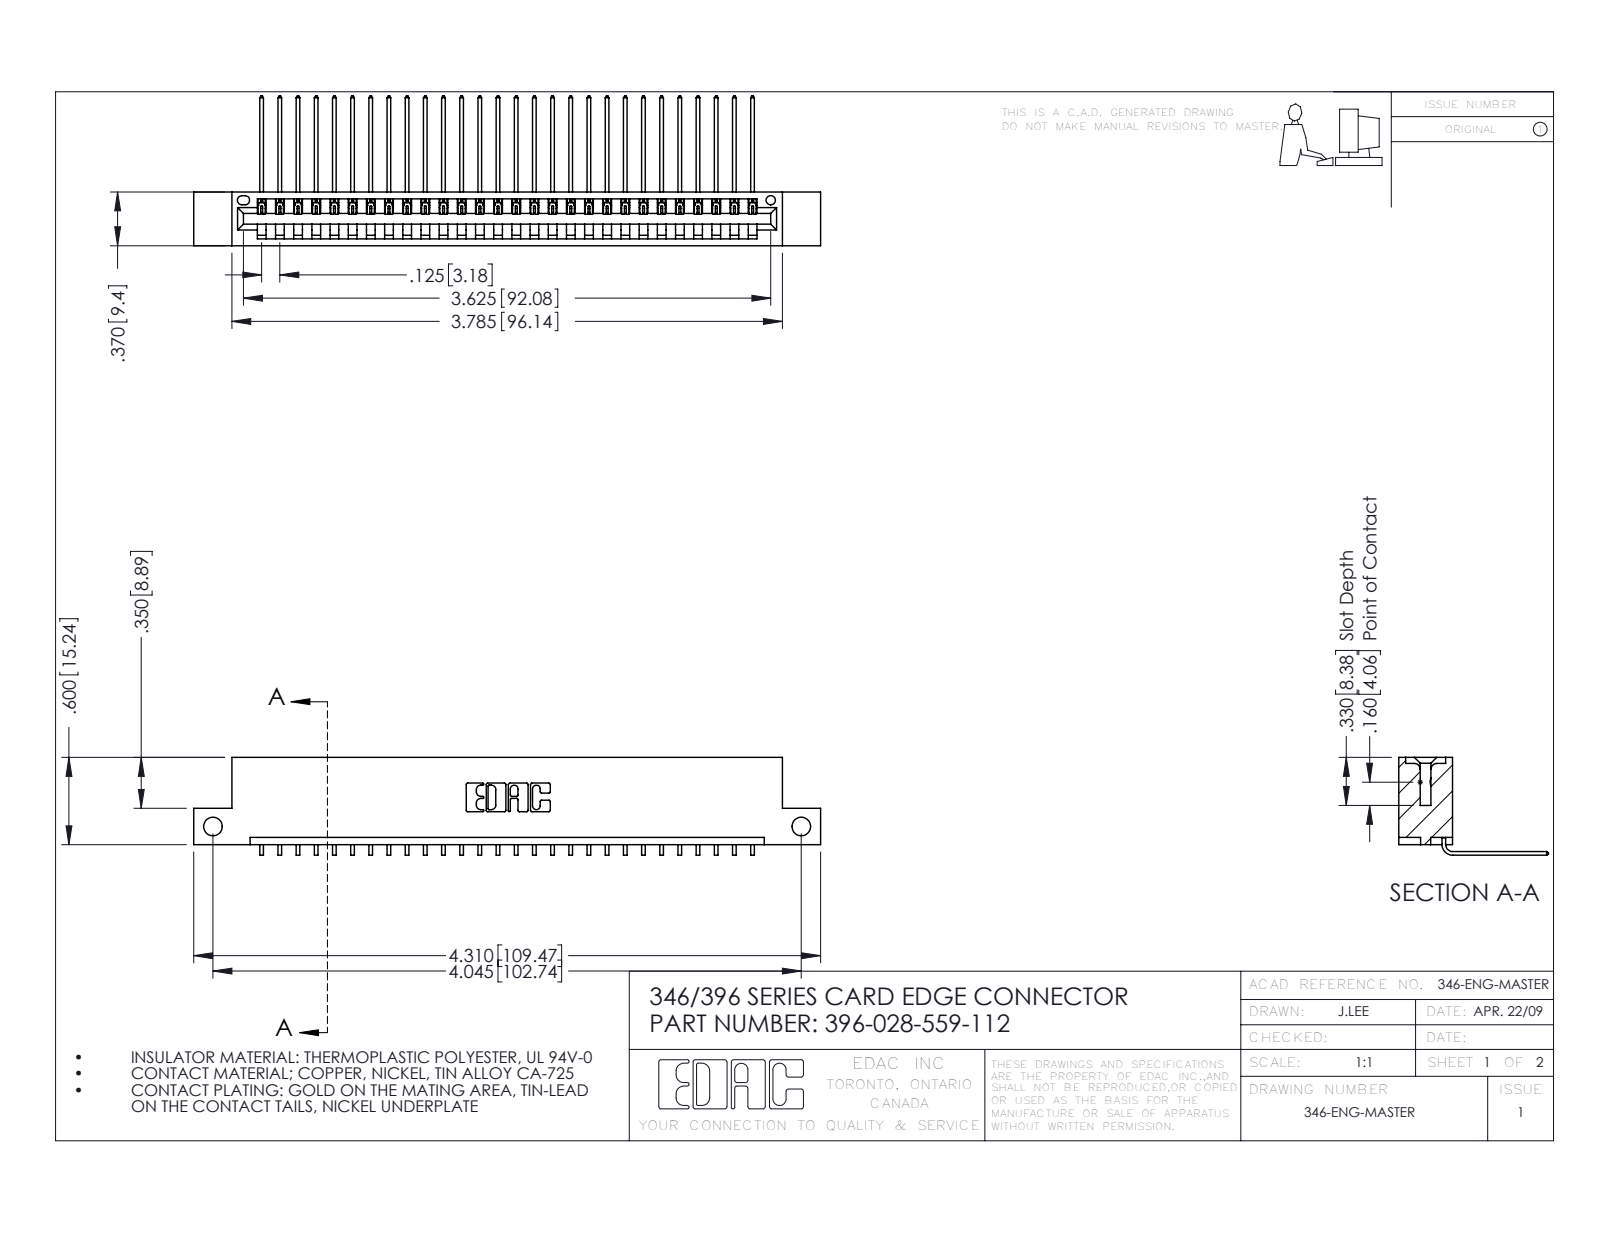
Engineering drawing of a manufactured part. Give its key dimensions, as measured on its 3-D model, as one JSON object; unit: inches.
{"part_name": "396-028-559-112; 346 Part_Flush Mounting Lugs - Side Mount; 345-292-001_558 559 Tail - 1", "step_written_by": "SolidWorks 2016 (CONFIG_CONTROL_DESIGN)", "units": "inches", "bodies": {"solids": 29, "faces": 1802, "planar": 1252, "cylindrical": 550, "other": 0}, "overall_size": [4.31, 1.03, 0.673], "volume_in3": 0.634, "surface_area_in2": 20.53, "round_holes": [[0.128, 2], [0.064, 1]], "partial_cylinders_radius": [[0.006, 56], [0.01, 22], [0.007, 6], [0.031, 6], [0.026, 3], [0.031, 2], [0.04, 2], [0.014, 1]], "face_to_face_distances": [0.048, 0.322, 0.37, 0.25, 0.072, 0.025, 0.298, 0.148, 0.222, 0.1], "hole_center_spacings": [4.045]}
